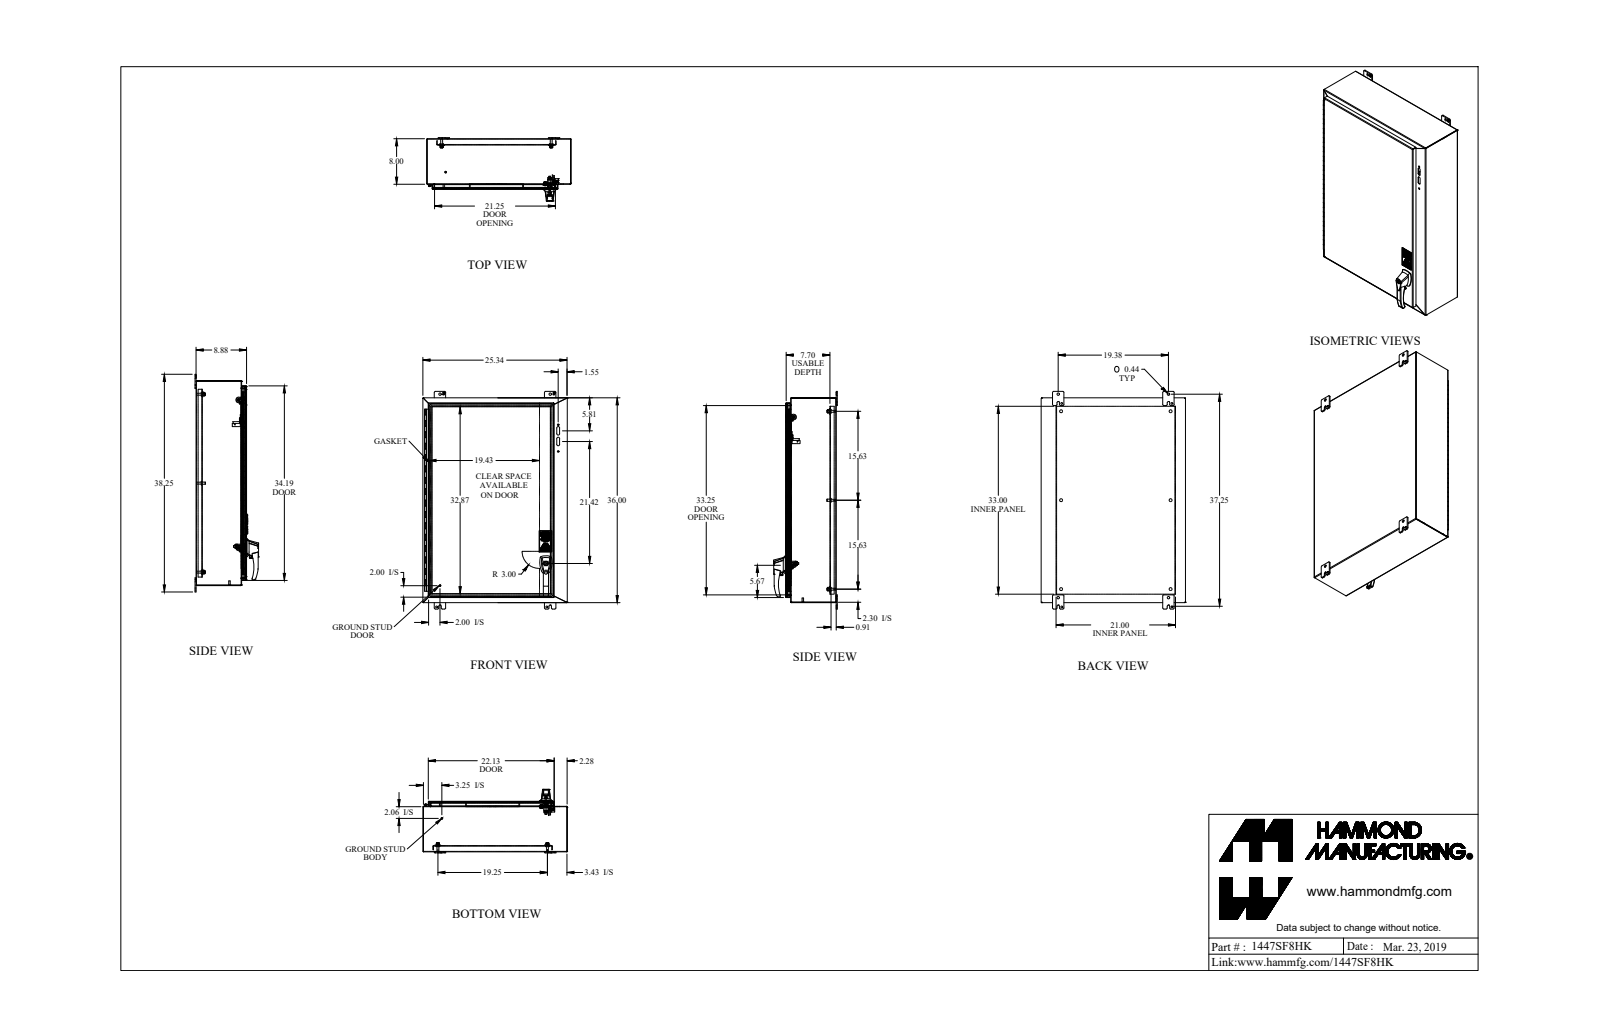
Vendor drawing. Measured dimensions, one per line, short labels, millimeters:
name: 1447SF8HK
written by: SolidWorks 2019 (AUTOMOTIVE_DESIGN)
unit: mm
bodies: 55 solids, 1279 faces (787 planar, 369 cylindrical, 123 other)
size: 971.54 × 644.53 × 283.9
volume: 5 286 000 mm³; area: 5 239 000 mm²
holes: 6× ⌀12.7, 5× ⌀7.94, 4× ⌀4.47, 4× ⌀7.81, 4× ⌀11.11, 4× ⌀11.3, 2× ⌀3.97, 2× ⌀4.39, 2× ⌀5.46, 2× ⌀6.35, 2× ⌀6.73, 2× ⌀7.14
bosses: 10× ⌀9.53, 7× ⌀6.35, 6× ⌀25.4, 6× ⌀16.51, 6× ⌀8.38, 4× ⌀3.97, 2× ⌀12.7, 2× ⌀10.21
rounds: 28× R2, 24× R4.76, 16× R0.17, 12× R6.35, 11× R3.17, 8× R0.76, 8× R3.83, 8× R5.54
face distances: 1.83, 223.6, 221.77, 225.43, 2.41, 197.39, 195.56, 26.21, 28.04, 199.8
hole spacings: 488.95, 396.88, 492.13, 629.75, 1032.83, 28.21, 44.08, 44.09
